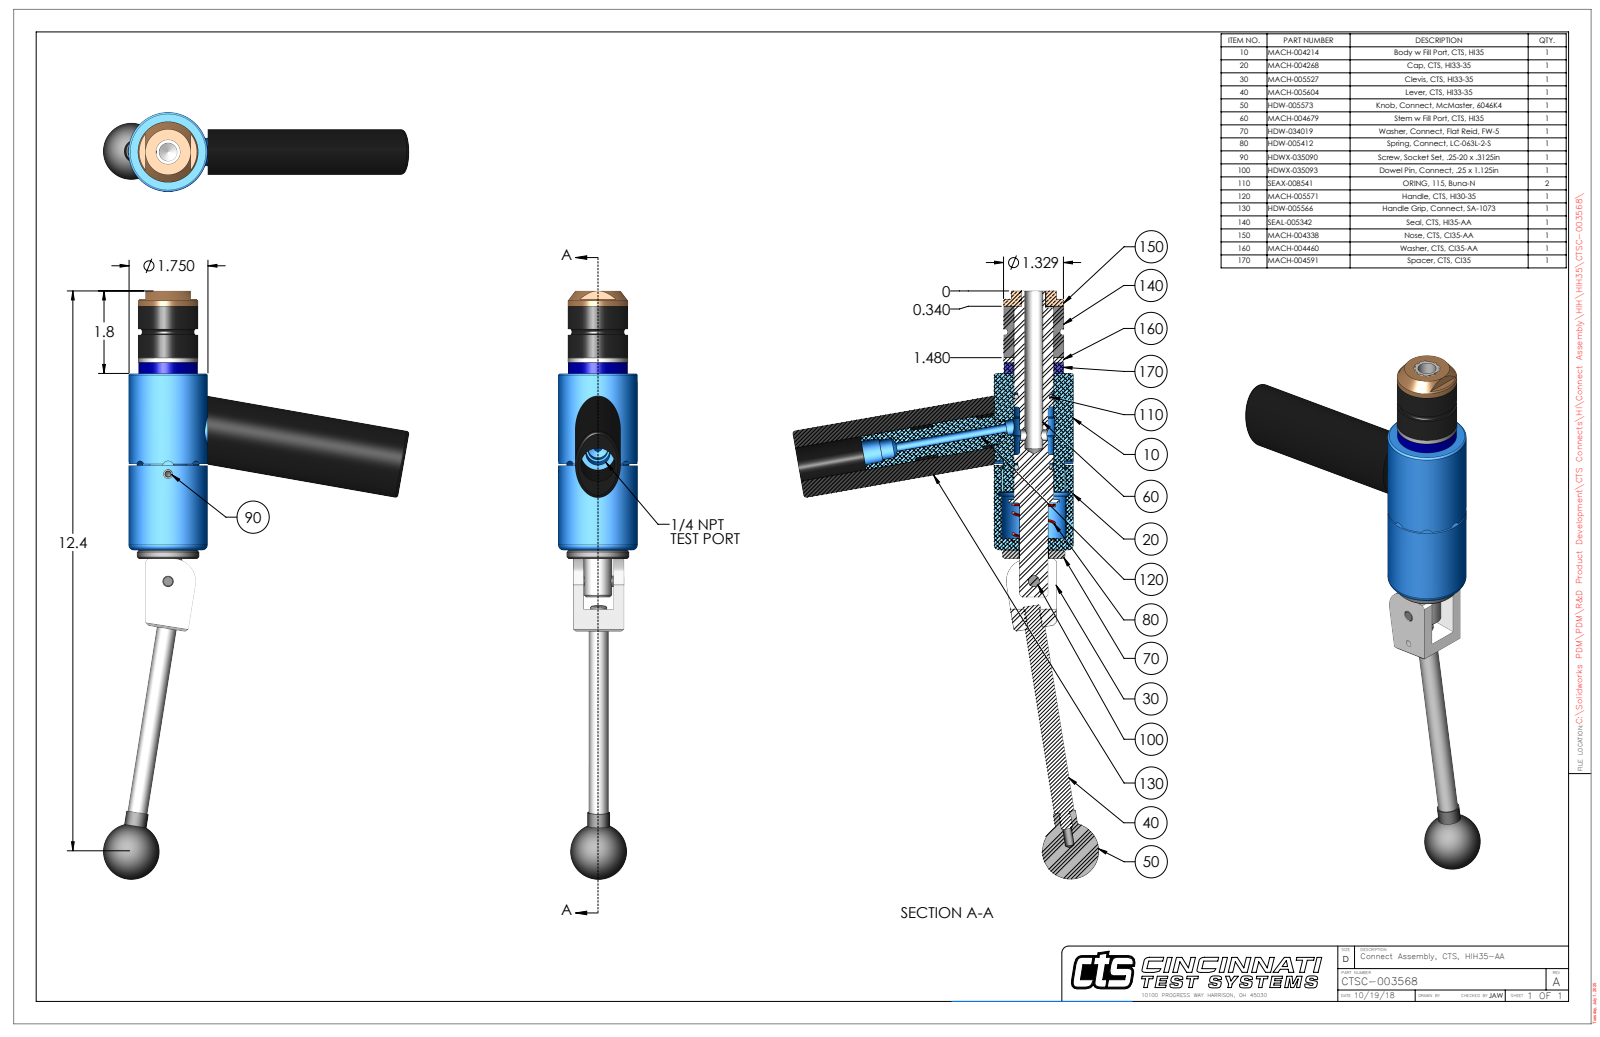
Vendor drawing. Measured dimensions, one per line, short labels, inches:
name: CTSC-003568
written by: SolidWorks 2023 (AUTOMOTIVE_DESIGN)
unit: in
bodies: 11 solids, 315 faces (112 planar, 131 cylindrical, 72 other)
size: 13.042 × 6.763 × 1.75
volume: 18.81 in³; area: 125.8 in²
holes: 2× ⌀0.201, 1× ⌀0.15, 1× ⌀0.187, 1× ⌀0.249, 1× ⌀0.25, 1× ⌀0.251, 1× ⌀0.313, 1× ⌀0.406, 1× ⌀0.438, 1× ⌀0.531, 1× ⌀0.635, 1× ⌀0.656
bosses: 2× ⌀0.25, 1× ⌀1.75, 1× ⌀1.38, 1× ⌀1.329, 1× ⌀1.312, 1× ⌀0.869, 1× ⌀0.75, 1× ⌀0.625
rounds: 4× R0.125, 2× R0.029, 1× R0.166, 1× R0.166, 1× R0.244, 1× R0.33, 1× R0.5, 1× R0.695
face distances: 3.915, 1.49, 5.405, 1.14, 0.35, 4.265, 1.25, 0.11, 0.24, 4.155
hole spacings: 0.74, 2.376, 3.116
